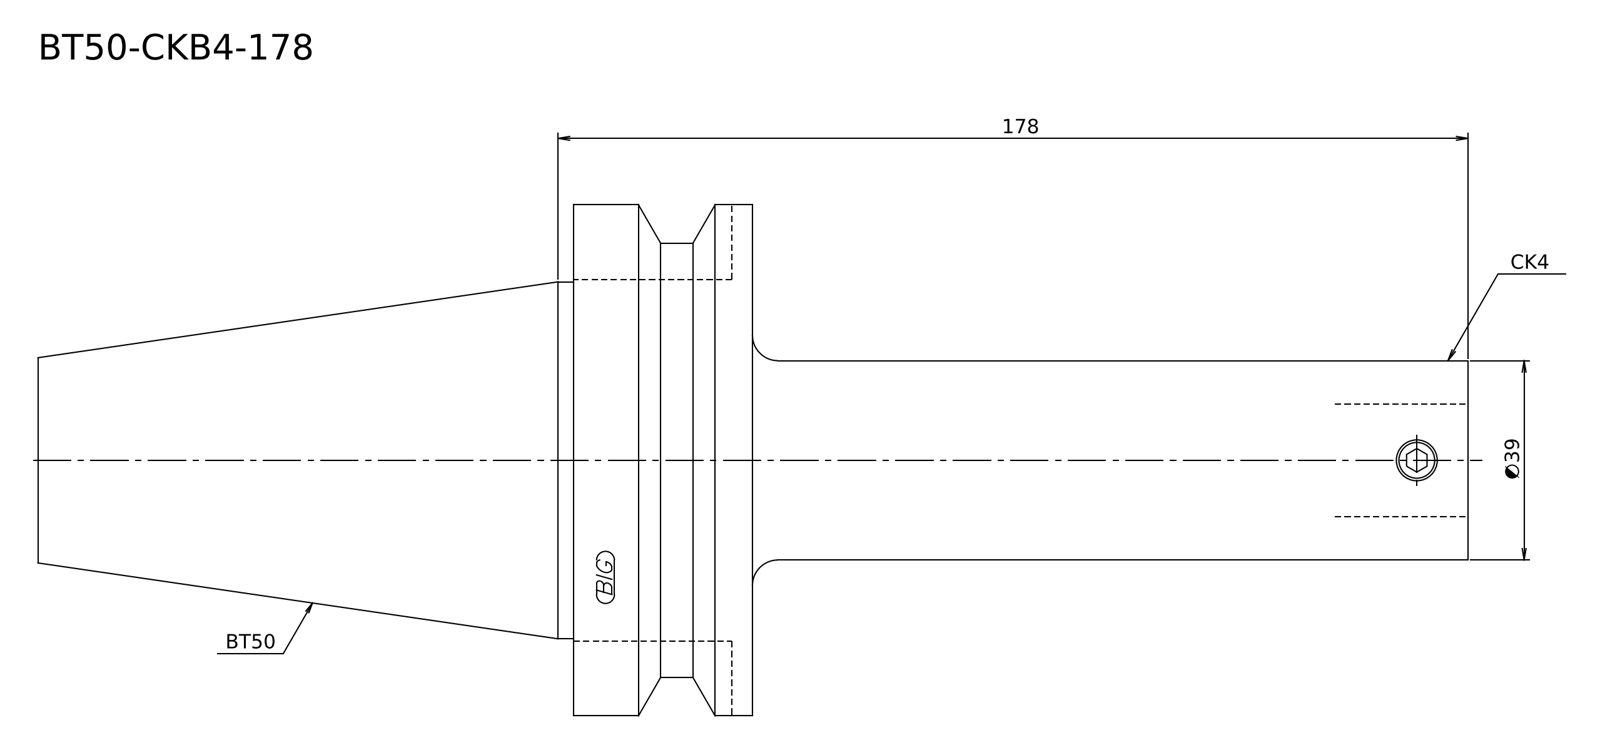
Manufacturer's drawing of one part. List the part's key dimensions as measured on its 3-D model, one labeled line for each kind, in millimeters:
STEP written by: Kubotek KeyCreator V8.5.1 (14335) (CONFIG_CONTROL_DESIGN)
Units: millimetres
Bodies: 1 solid, 13 faces (4 planar, 5 cylindrical, 4 other)
Overall size (bounding box): 279.8 × 100 × 100
Volume: 679 551 mm³ · Surface area: 61 414 mm²
Round bosses / shafts (diameter × count): ⌀100 ×1, ⌀85 ×1, ⌀69.85 ×1, ⌀39 ×1
Main face-to-face distances: 35, 139.8, 104.8, 140, 175, 279.8
